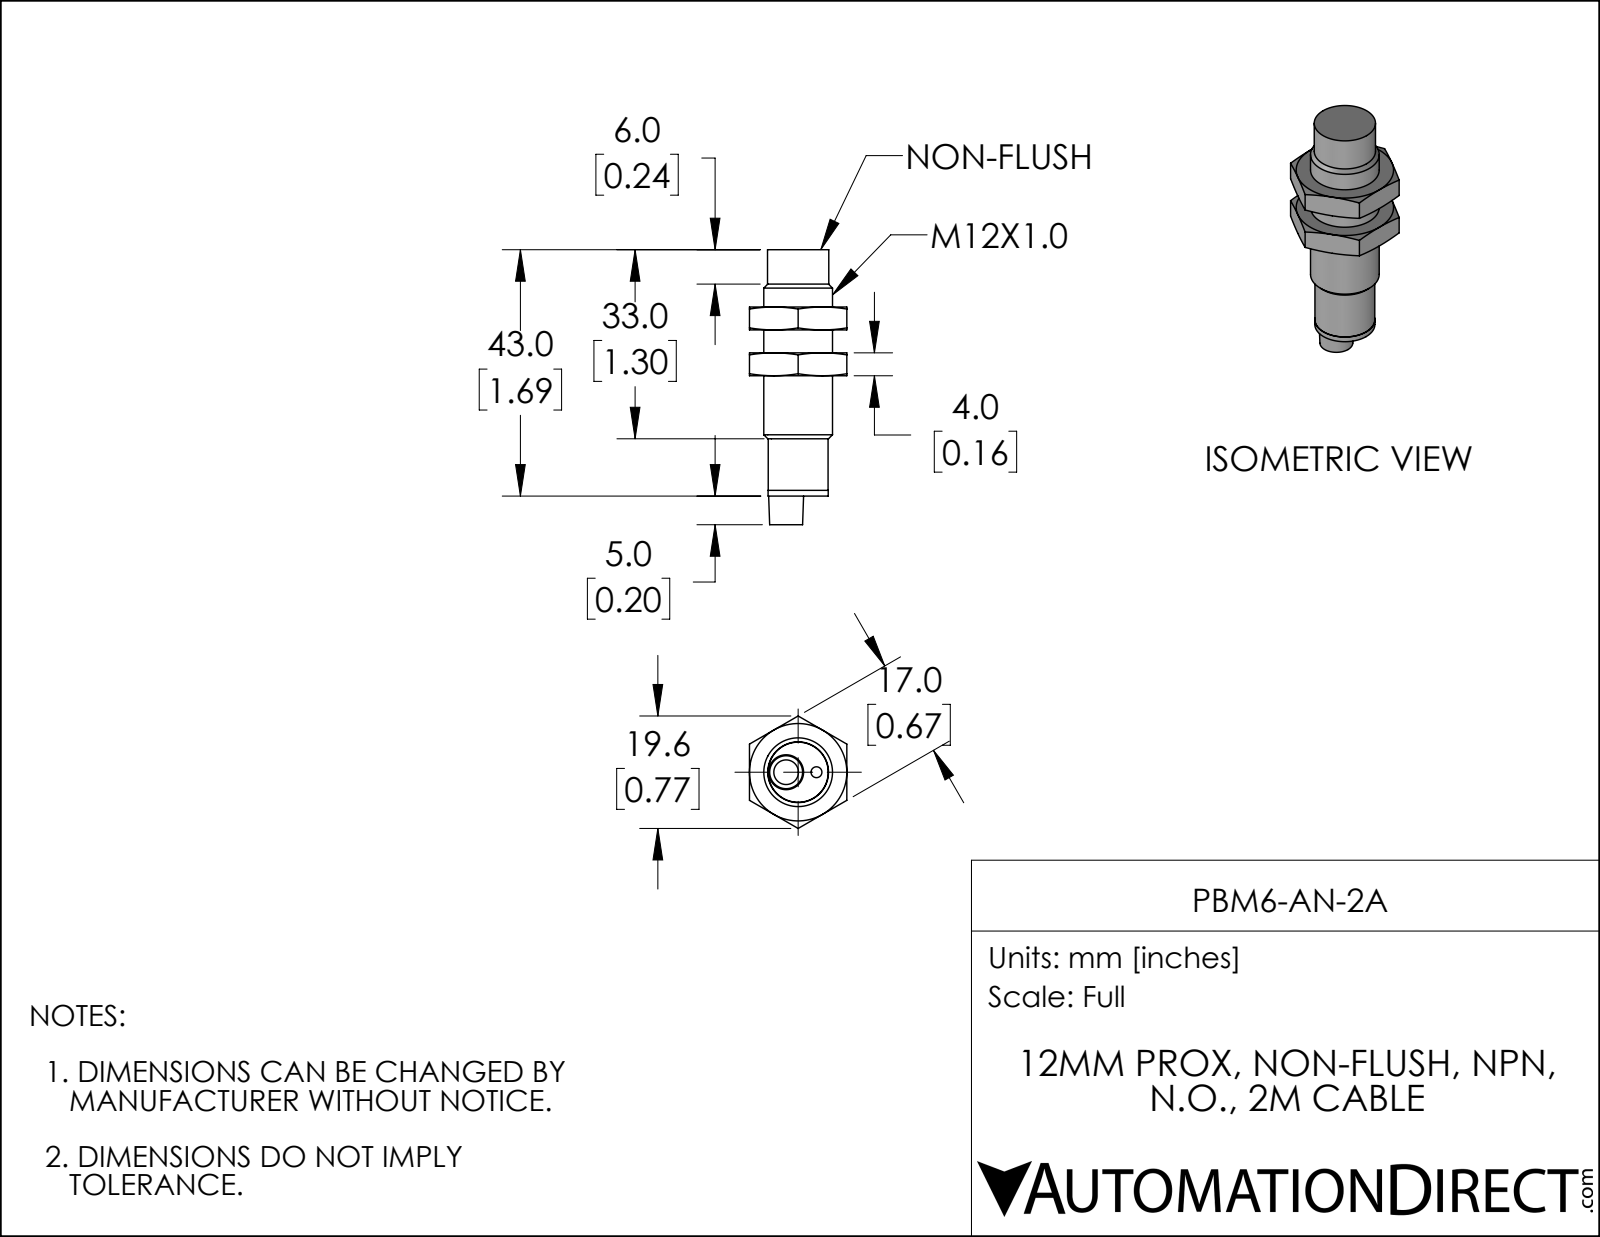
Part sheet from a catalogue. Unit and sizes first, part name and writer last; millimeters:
Units: millimetres
Overall size (bounding box): 48 × 12 × 12
Round holes (diameter × count): ⌀1.9 ×1, ⌀4.3 ×1
Round bosses / shafts (diameter × count): ⌀12 ×1, ⌀10.7 ×1, ⌀10.5 ×1, ⌀10.45 ×1
Main face-to-face distances: 43, 41.98, 1.02, 48, 6.02, 5, 6, 42, 1, 33
Hole centre spacings: 5.3
Volume: 4 482 mm³ · Surface area: 1 924 mm²
Bodies: 1 solid, 17 faces (8 planar, 6 cylindrical, 3 other)
Part name (STEP PRODUCT): DSD-0276
STEP written by: SolidWorks 2019 (AUTOMOTIVE_DESIGN)
